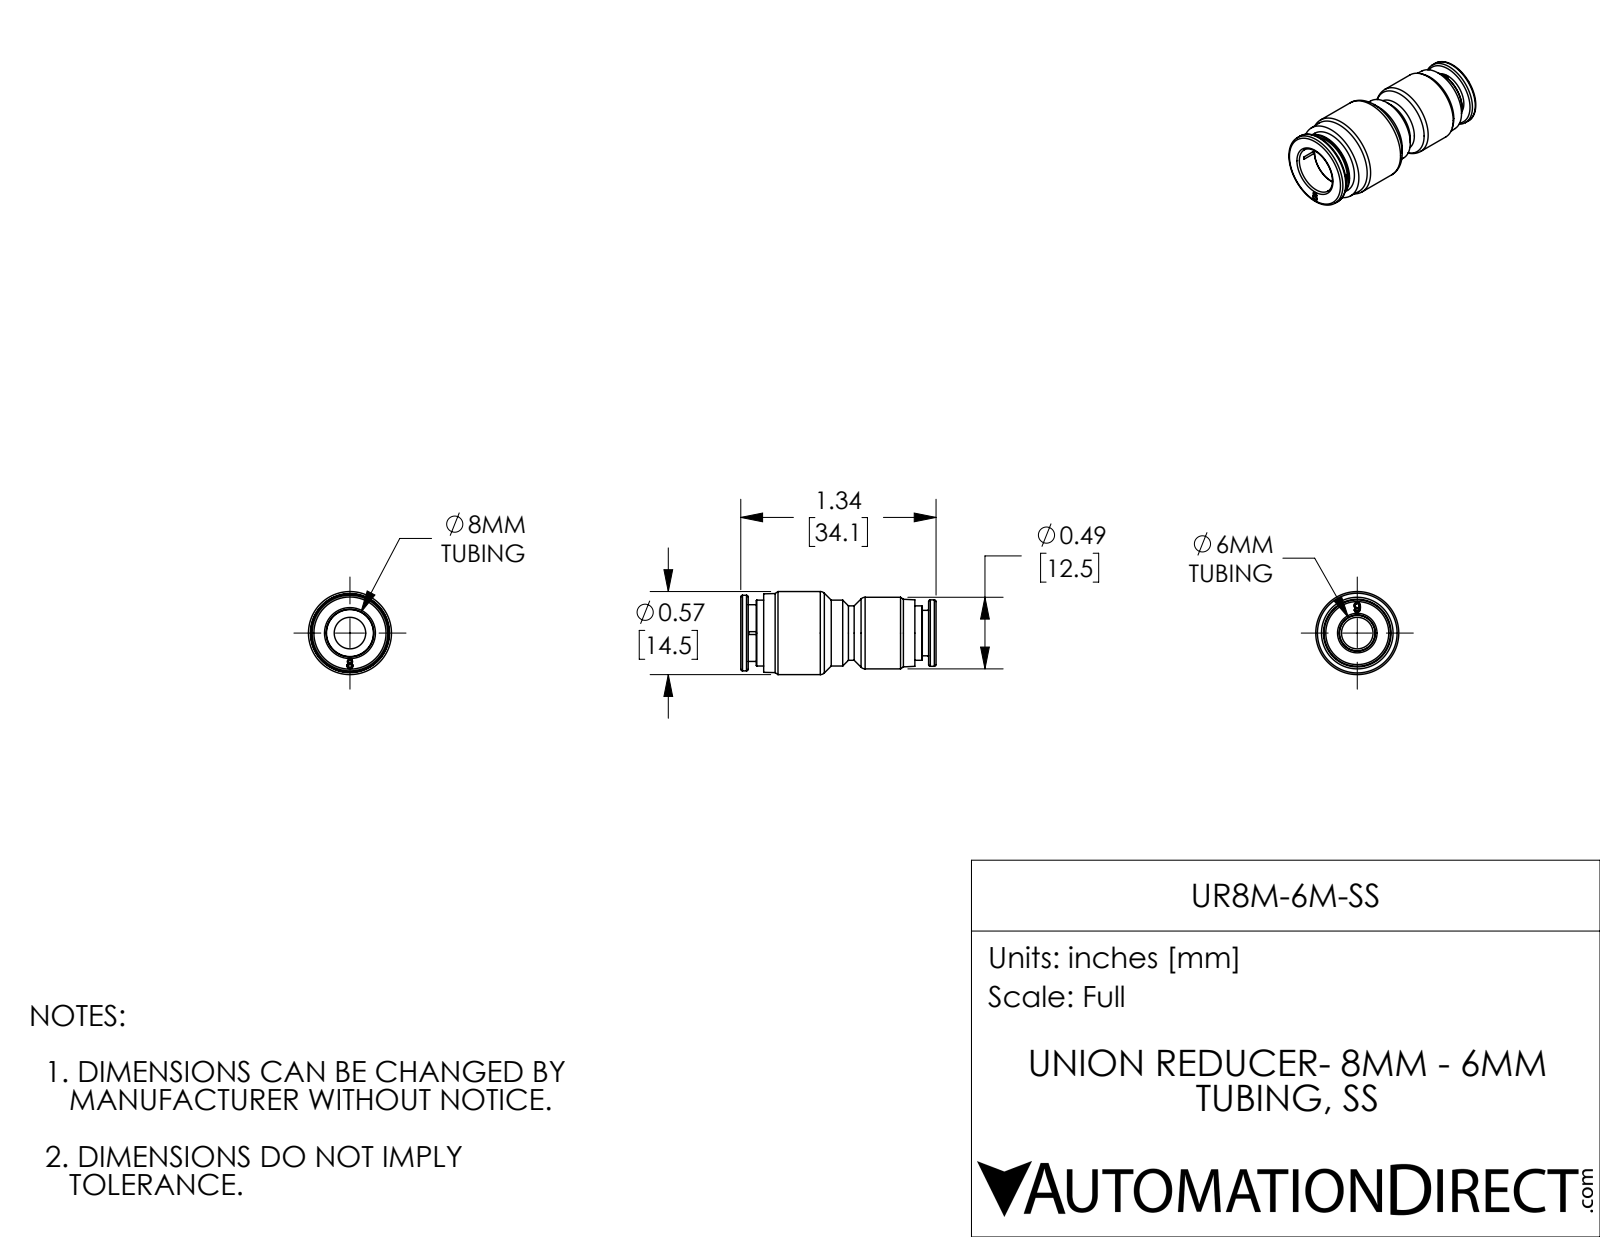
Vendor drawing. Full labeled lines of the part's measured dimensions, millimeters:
Part name (STEP PRODUCT): UR8M-6M-SS
STEP written by: SolidWorks 2017 (AUTOMOTIVE_DESIGN)
Units: millimetres
Bodies: 1 solid, 132 faces (30 planar, 34 cylindrical, 68 other)
Overall size (bounding box): 34.1 × 14.5 × 14.5
Volume: 2 720 mm³ · Surface area: 2 715 mm²
Round holes (diameter × count): ⌀5.5 ×1, ⌀6.2 ×1, ⌀6.3 ×1, ⌀8.1 ×1, ⌀8.2 ×1, ⌀8.3 ×1, ⌀10 ×1
Round bosses / shafts (diameter × count): ⌀14.5 ×1, ⌀13.2 ×1, ⌀12.5 ×1, ⌀11.6 ×1, ⌀11.5 ×1, ⌀9.9 ×1, ⌀9.5 ×1, ⌀8 ×1
Main face-to-face distances: 1.3, 32.8, 30.1, 2.7, 34.1, 4, 2.4, 30.4, 31.5, 28.8
